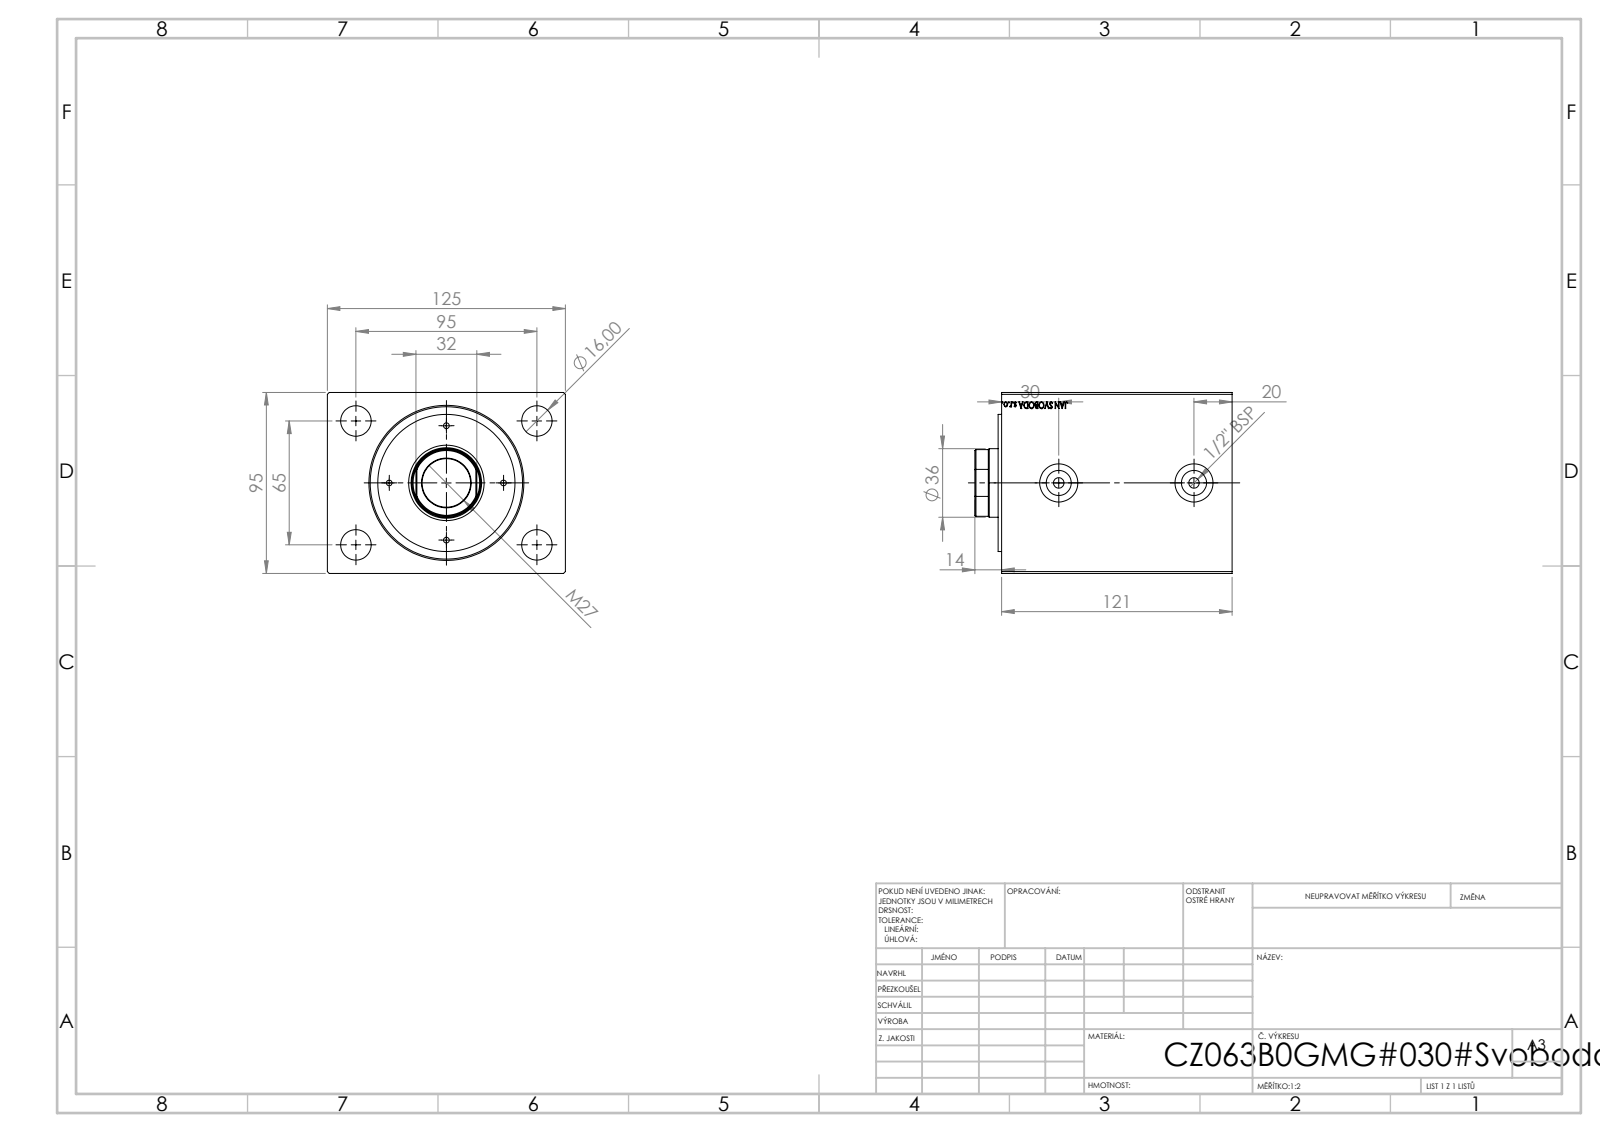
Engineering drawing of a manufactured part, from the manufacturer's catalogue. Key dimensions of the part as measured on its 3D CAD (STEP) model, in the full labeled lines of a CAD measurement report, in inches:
Part name (STEP PRODUCT): V500CZ_B_VC; V500CZ
STEP written by: SolidWorks 2019 (CONFIG_CONTROL_DESIGN)
Units: inches
Bodies: 3 solids, 874 faces (400 planar, 58 cylindrical, 416 other)
Overall size (bounding box): 5.315 × 4.921 × 3.74
Volume: 80.25 in³ · Surface area: 231.2 in²
Round holes (diameter × count): ⌀0.118 ×4, ⌀0.63 ×4, ⌀0.217 ×2, ⌀0.518 ×2, ⌀0.787 ×2, ⌀1.004 ×1, ⌀1.417 ×1, ⌀1.457 ×1, ⌀2.48 ×1, ⌀3.15 ×1
Round bosses / shafts (diameter × count): ⌀2.835 ×1
Partial cylindrical surfaces — rounded edges, fillets, slot ends (radius × count): R0.689 ×1
Main face-to-face distances: 3.74, 4.921, 4.764, 3.945, 0.819, 0.551, 0.071, 0.48, 3.465, 4.283
Hole centre spacings: 1.181, 1.453, 1.67, 1.873, 2.266, 3.091, 3.309, 2.362
